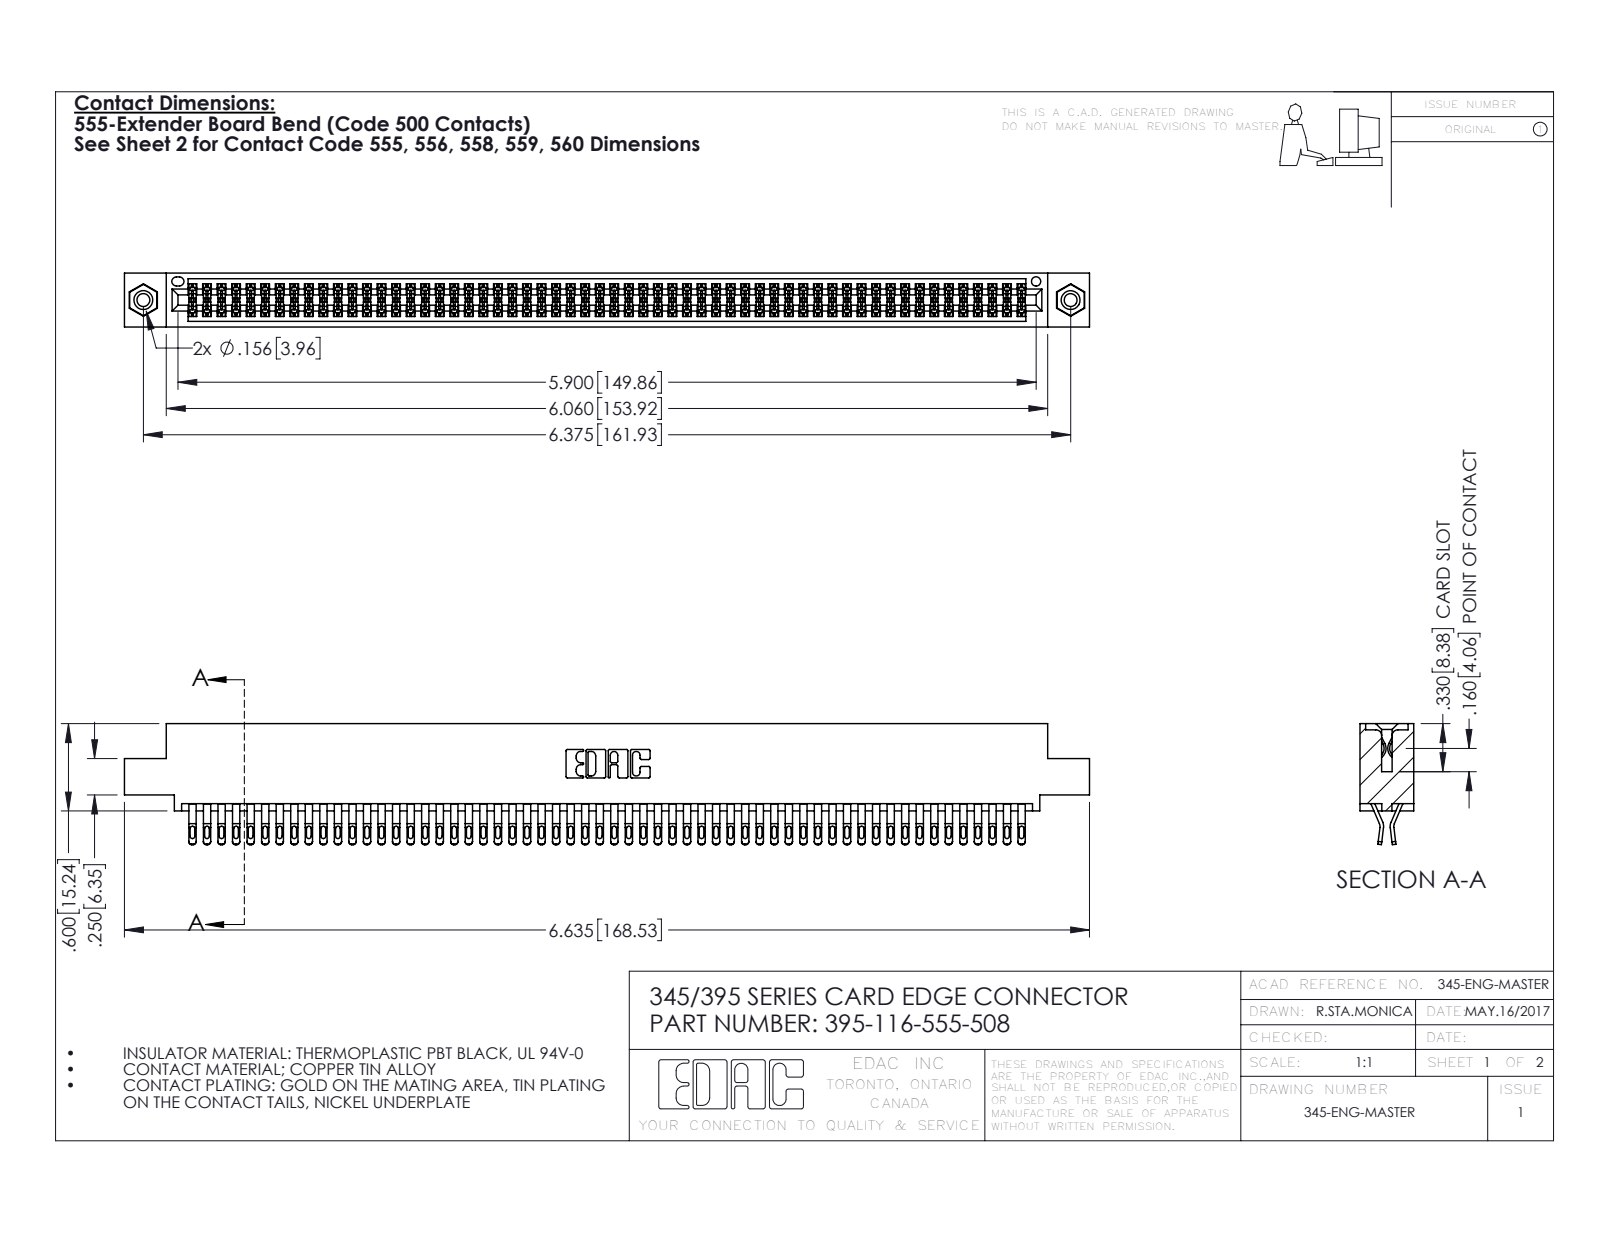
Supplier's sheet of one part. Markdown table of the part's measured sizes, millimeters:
| quantity | value |
| --- | --- |
| part name | 395-116-555-508; 345 Part_0.110 Offset - 0.156 Dia-TI; 345-250-001_345-250-003-102; 345-292-001_555 Tail |
| STEP written by | SolidWorks 2016 (CONFIG_CONTROL_DESIGN) |
| units | millimeters |
| bodies | 119 solids, 6686 faces (3712 planar, 2958 cylindrical, 16 other) |
| overall size | 168.5 × 21.1 × 9.4 |
| volume | 16 780 mm³ |
| surface area | 26 390 mm² |
| round holes (diameter × count) | 2.3 × 2, 3.2 × 2, 4 × 2, 1.6 × 1 |
| round bosses / shafts (diameter × count) | 3.9 × 2 |
| partial cylindrical surfaces (radius × count) | 0.4 × 290, 0.5 × 232, 0.2 × 174, 0.3 × 22, 0.2 × 6, 0.8 × 6, 0.7 × 3, 0.3 × 2 |
| main face-to-face distances | 1.8, 7.6, 0.6, 9.4, 5.1, 2.5, 6.9, 5.7, 4.4, 3.8 |
| hole center spacings | 6.9, 155.9, 161.9 |
